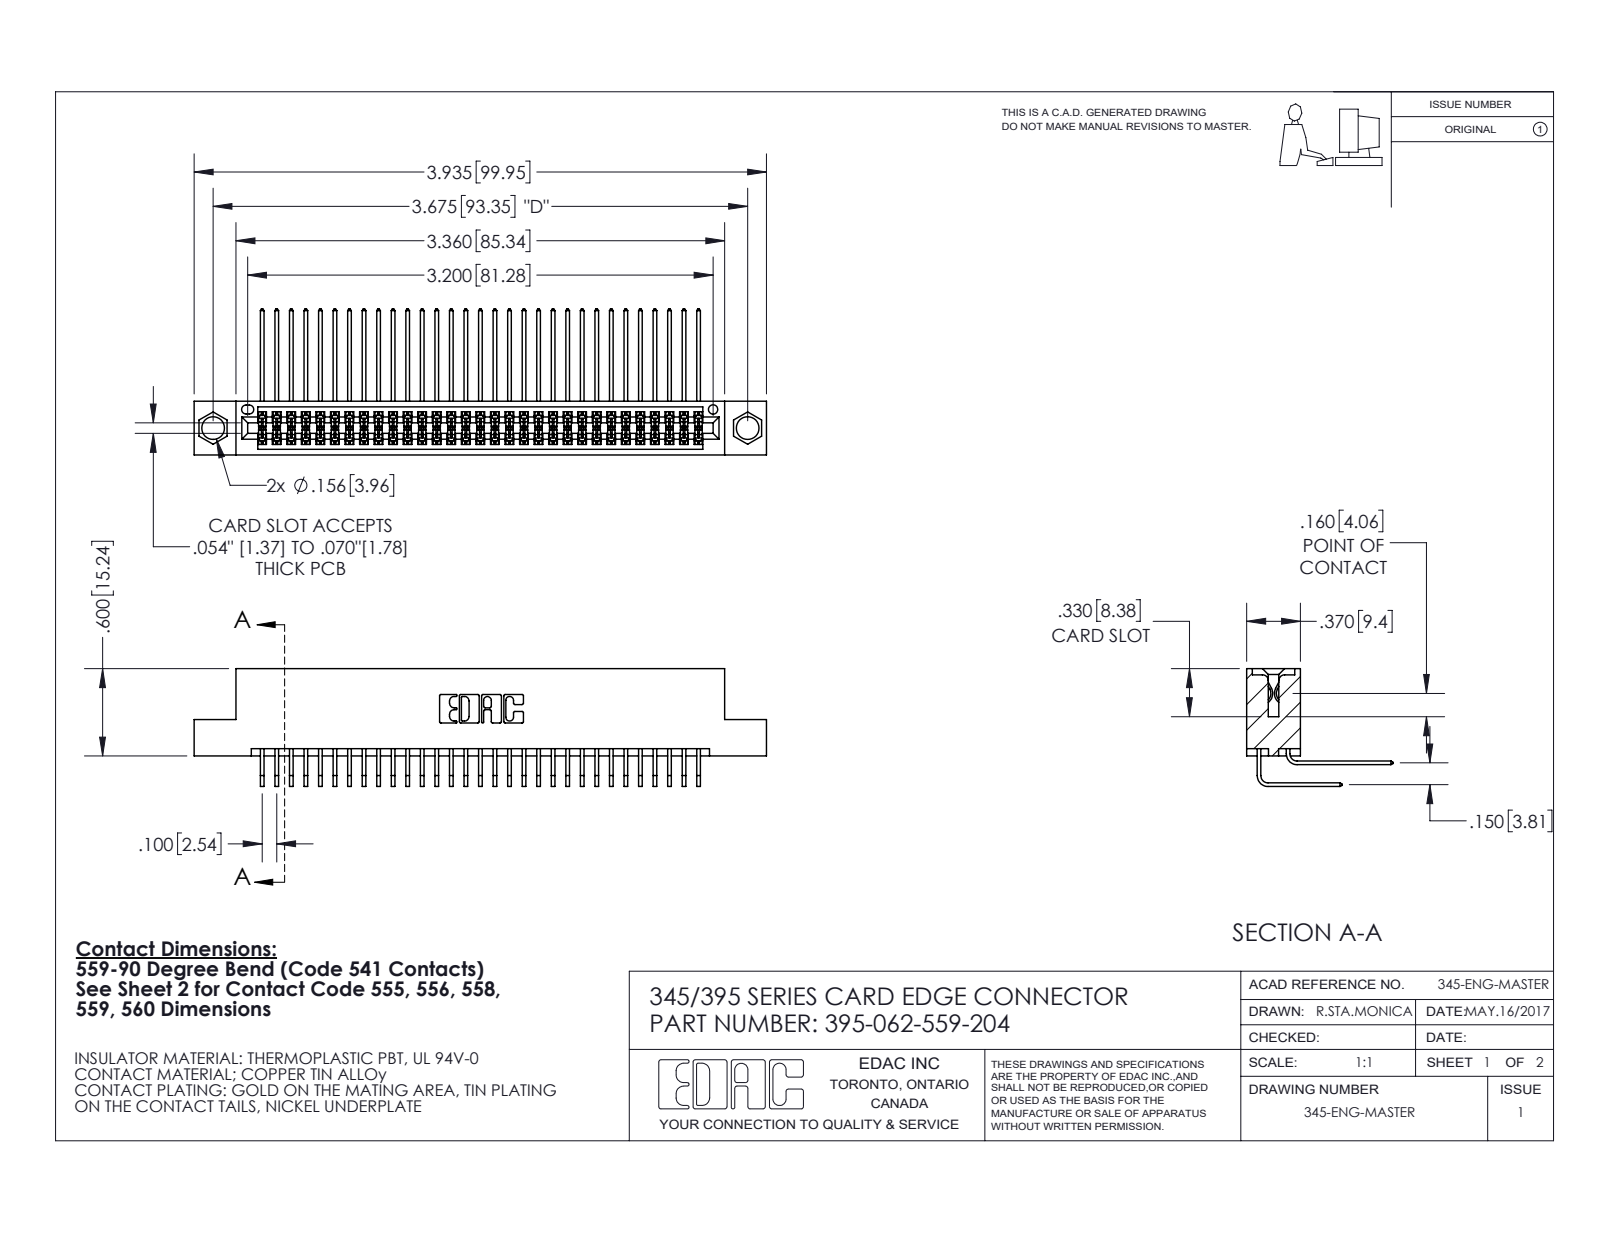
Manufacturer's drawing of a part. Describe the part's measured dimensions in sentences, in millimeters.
The part is named "345-292-001_559 Tail - 2; 345 Part_Flush Mounting Lugs - 0.156 Dia-TI; 395-062-559-204; 345-292-001_558 559 Tail - 1". Its 3-D file was written by "SolidWorks 2020 (CONFIG_CONTROL_DESIGN)". It is 63 solids with 3364 faces: 2264 planar, 1100 cylindrical and 0 other. Overall it measures 99.9 by 25.5 by 20.5 millimeters. Its volume is 9 870 cubic millimeters and its surface area 15 890 square millimeters. Round holes: 2 of diameter 4, 1 of diameter 1.6. Partial cylindrical surfaces (rounded edges, fillets, slot ends): 93 of radius 0.2, 22 of radius 0.3, 6 of radius 0.2, 6 of radius 0.8, 3 of radius 0.7, 2 of radius 0.4, 2 of radius 0.5, 2 of radius 0.6. The main face-to-face distances are 1.8, 7.6, 5.1, 9.4, 2.5, 6.9, 0.6, 5.7, 3.8, 4.4. The hole center spacings are 6.9, 87.4, 93.3.
